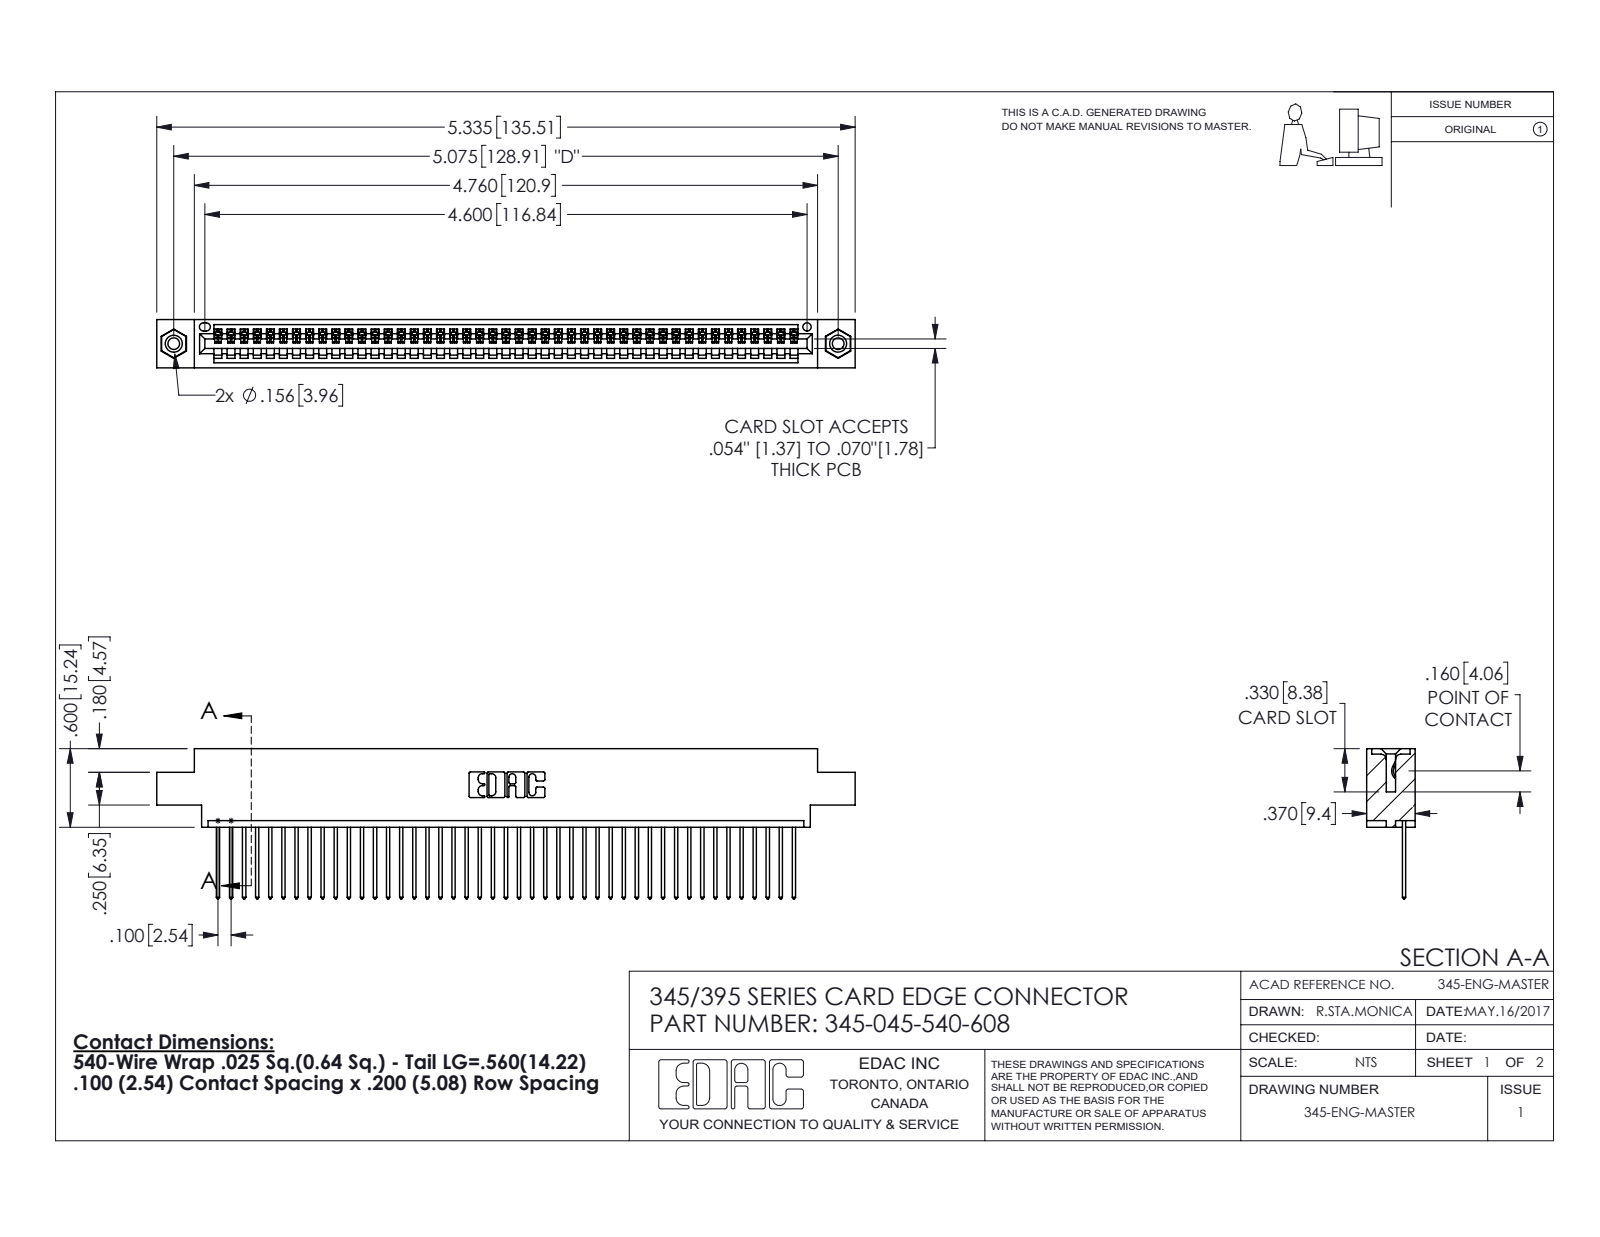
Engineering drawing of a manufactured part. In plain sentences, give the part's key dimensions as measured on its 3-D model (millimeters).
The part is named "345-292-001_345-293-140; 345-045-540-608; 345 Part_0.170 Offset - 0.156 Dia-TI; 345-250-001_345-250-003-102". Its 3-D file was written by "SolidWorks 2016 (CONFIG_CONTROL_DESIGN)". It is 48 solids with 2800 faces: 1916 planar, 868 cylindrical and 16 other. Overall it measures 135.5 by 29.1 by 9.4 millimeters. Its volume is 12 800 cubic millimeters and its surface area 17 680 square millimeters. Round holes: 2 of diameter 2.3, 2 of diameter 3.2, 2 of diameter 4, 1 of diameter 1.6. Round bosses or shafts: 2 of diameter 3.9. Partial cylindrical surfaces (rounded edges, fillets, slot ends): 90 of radius 0.2, 90 of radius 0.3, 22 of radius 0.3, 6 of radius 0.2, 6 of radius 0.8, 3 of radius 0.7, 2 of radius 0.8, 2 of radius 1. The main face-to-face distances are 1.8, 7.6, 9.4, 2.5, 6.9, 0.6, 5.1, 5.7, 4.4, 3.8. The hole center spacings are 6.9, 122.9, 128.9.
